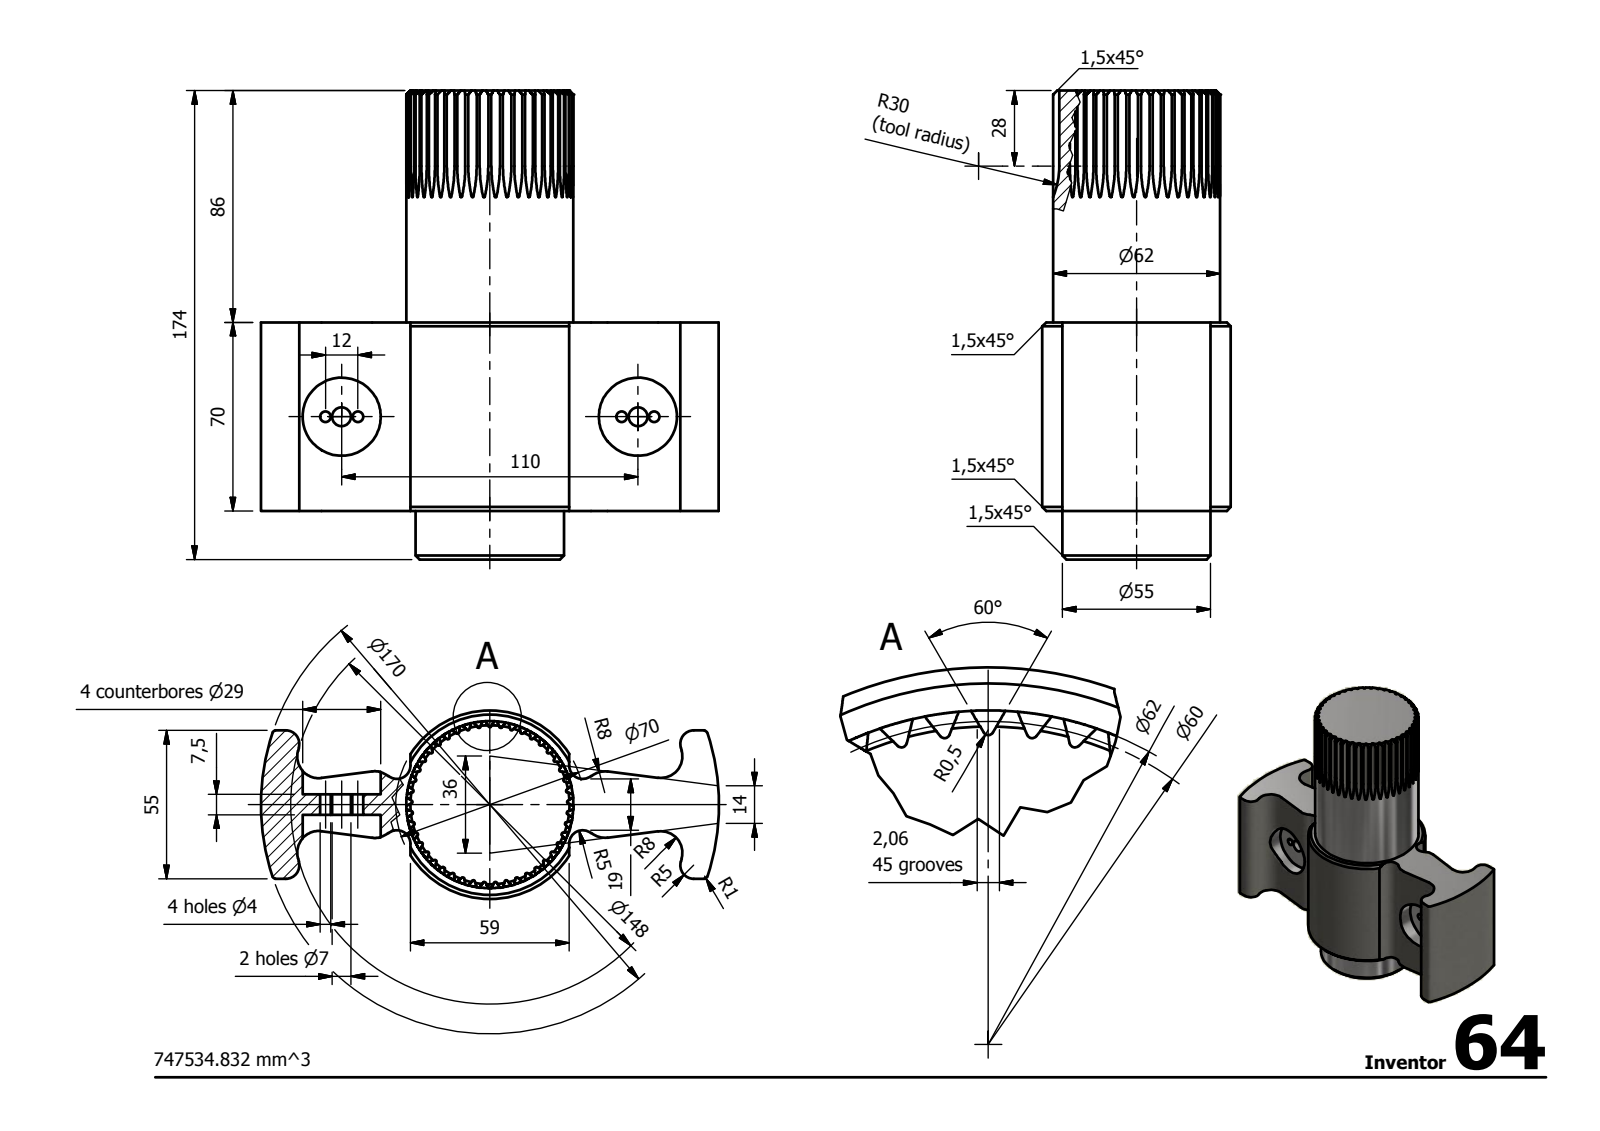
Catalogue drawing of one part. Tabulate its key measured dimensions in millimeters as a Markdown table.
| quantity | value |
| --- | --- |
| STEP written by | Autodesk Inventor 2014 (AUTOMOTIVE_DESIGN) |
| units | millimeters |
| bodies | 1 solid, 384 faces (114 planar, 85 cylindrical, 185 other) |
| overall size | 174 × 170 × 70 |
| volume | 747 689 mm³ |
| surface area | 77 582 mm² |
| round holes (diameter × count) | 4 × 4, 7 × 2, 29 × 2 |
| round bosses / shafts (diameter × count) | 62 × 1, 55 × 1 |
| partial cylindrical surfaces (radius × count) | 0.5 × 45, 5 × 8, 8 × 8, 1 × 4, 35 × 1, 74 × 1, 85 × 1 |
| main face-to-face distances | 70, 156, 86, 18, 88, 174, 7.5, 23.75, 31.25, 35.74 |
| hole center spacings | 6, 110, 12, 104, 116, 98, 122 |
